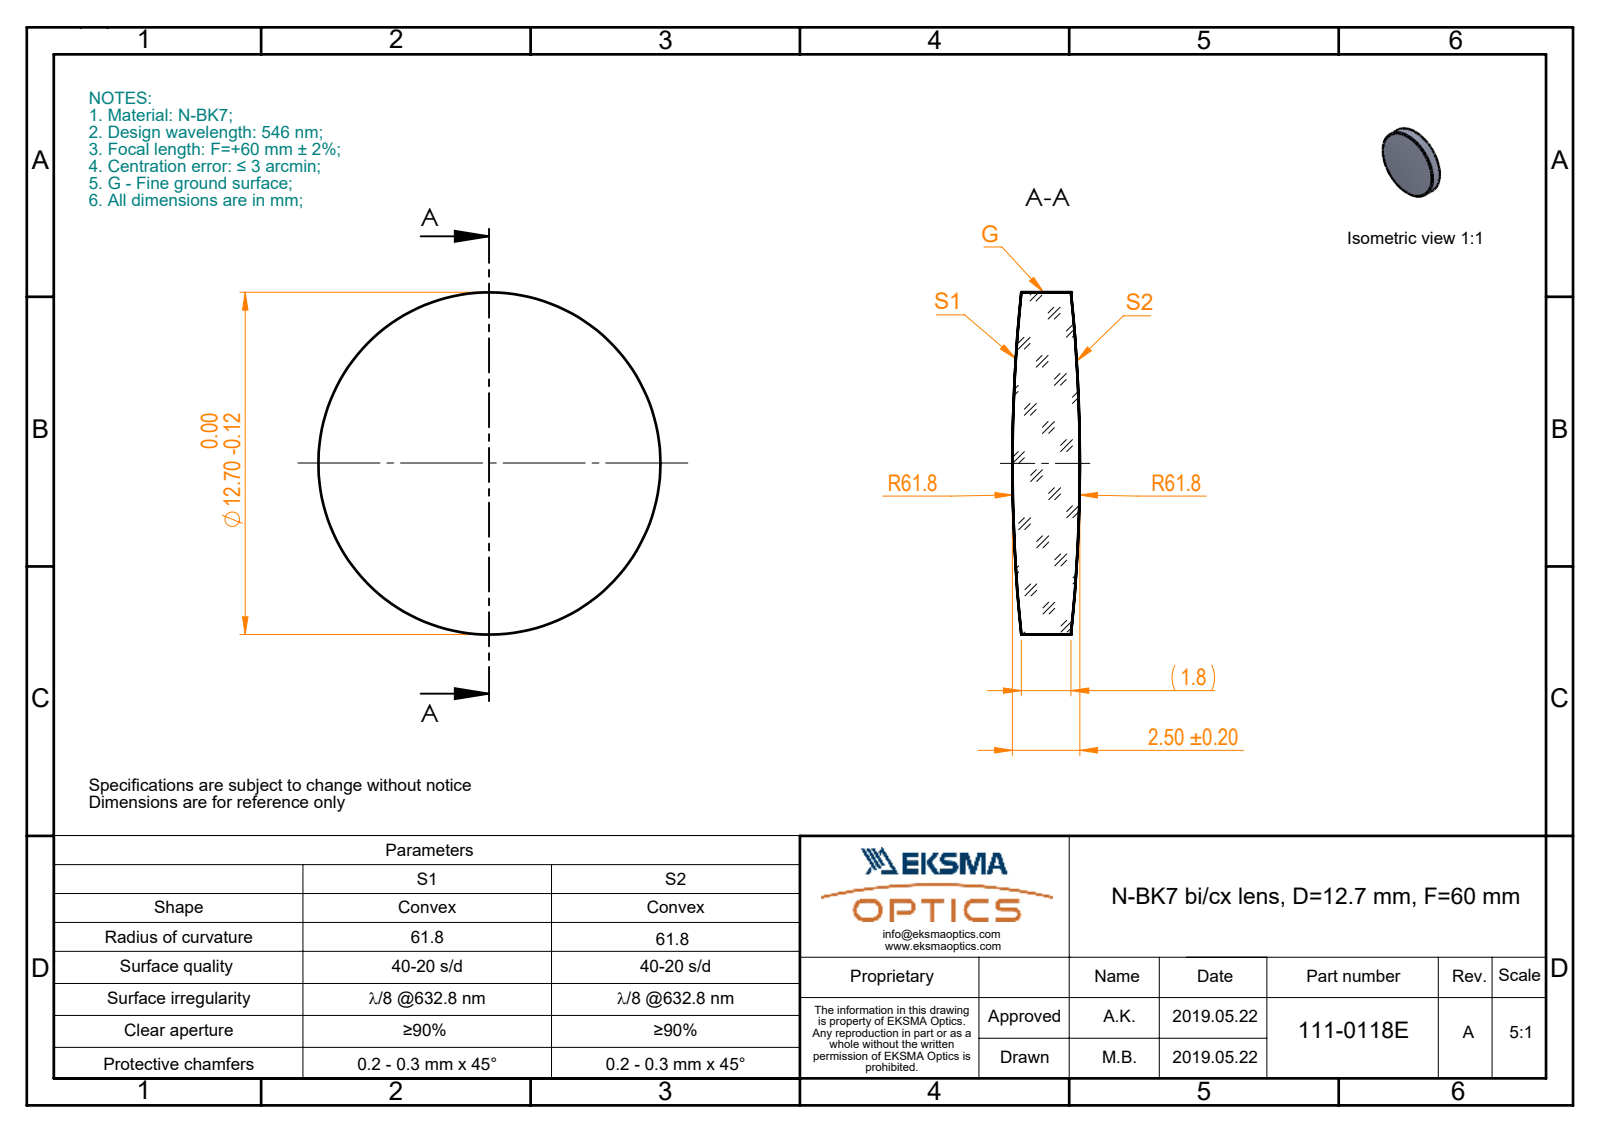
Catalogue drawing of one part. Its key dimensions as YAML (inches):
part_name: "111-0118E BK7 bi-cx 12.7 F60"
step_written_by: "SolidWorks 2017 (CONFIG_CONTROL_DESIGN)"
units: inches
bodies: {solids: 1, faces: 6, planar: 0, cylindrical: 2, other: 4}
overall_size: [0.5, 0.5, 0.098]
volume: 0.017
surface_area: 0.508
round_bosses_or_shafts:
  - {diameter: 0.5, count: 1}
